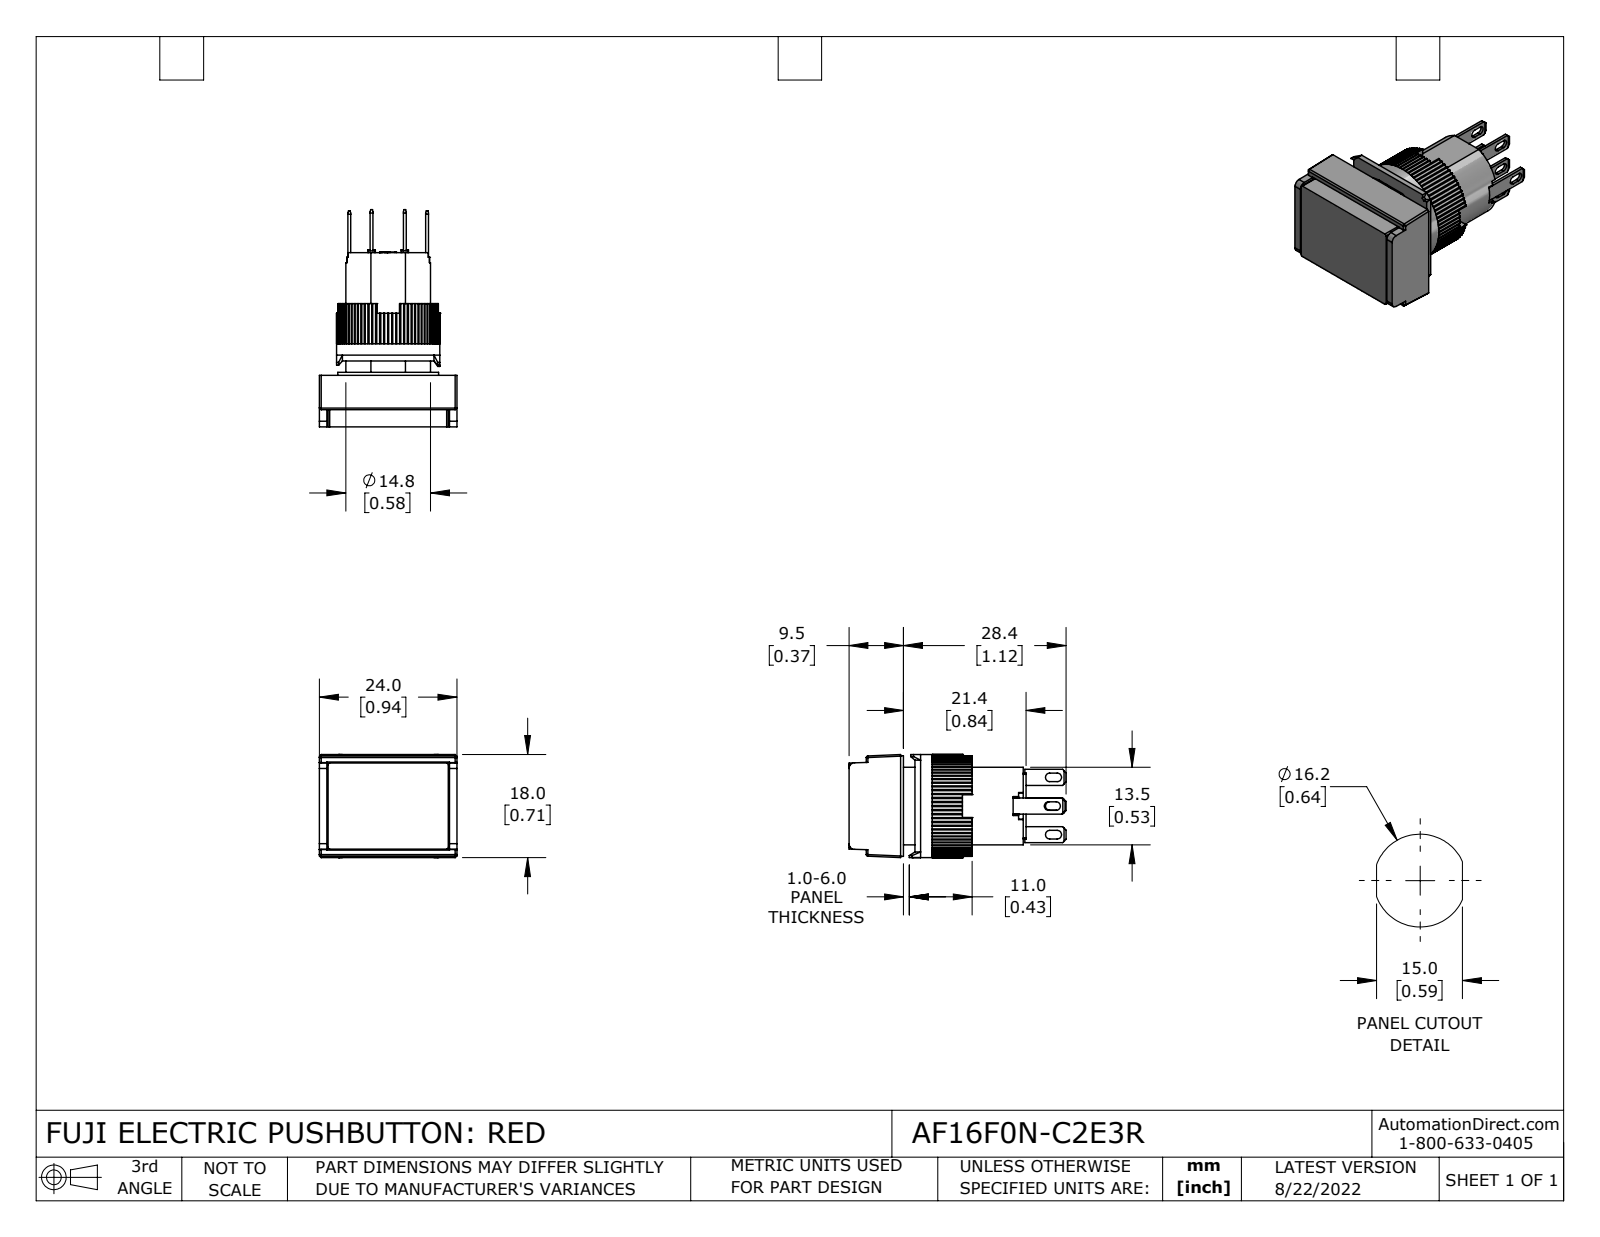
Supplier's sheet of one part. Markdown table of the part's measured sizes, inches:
| quantity | value |
| --- | --- |
| part name | AF16F0N-C2E3R |
| STEP written by | SolidWorks 2023 (CONFIG_CONTROL_DESIGN) |
| units | inches |
| bodies | 14 solids, 845 faces (656 planar, 185 cylindrical, 4 other) |
| overall size | 1.492 × 0.945 × 0.709 |
| volume | 0.469 in³ |
| surface area | 9.459 in² |
| round holes (diameter × count) | 0.543 × 1, 0.583 × 1 |
| round bosses / shafts (diameter × count) | 0.709 × 1, 0.693 × 1 |
| partial cylindrical surfaces (radius × count) | 0.01 × 80, 0.008 × 12, 0.03 × 8, 0.012 × 6, 0.039 × 2, 0.315 × 1 |
| main face-to-face distances | 0.213, 0.354, 0.142, 0.35, 0.492, 0.705, 0.138, 0.02, 0.843, 0.764 |
